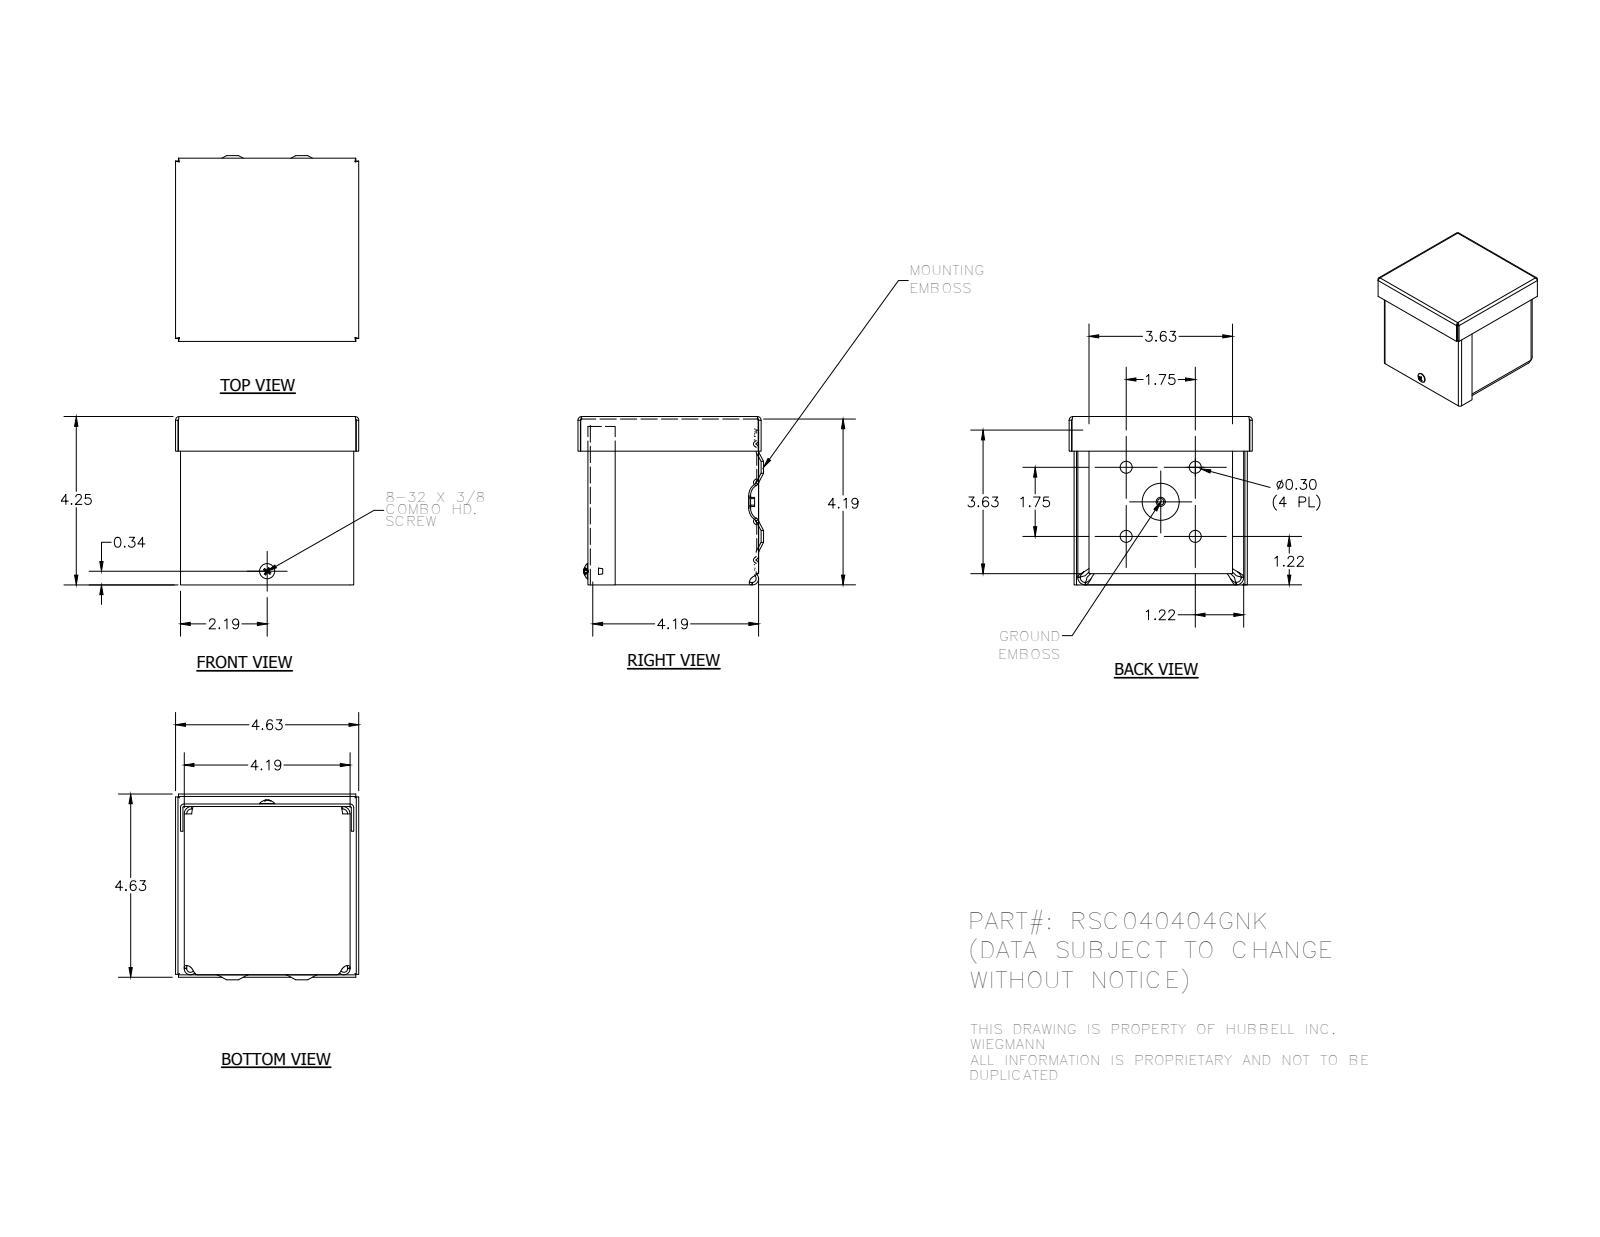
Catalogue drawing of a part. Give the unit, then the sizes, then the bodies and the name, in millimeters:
Units: millimetres
Overall size (bounding box): 119.09 × 117.47 × 107.96
Round holes (diameter × count): ⌀7.62 ×4, ⌀7.95 ×2, ⌀3.76 ×1, ⌀4.19 ×1
Round bosses / shafts (diameter × count): ⌀9.75 ×1, ⌀5.8 ×1, ⌀4.17 ×1
Partial cylindrical surfaces — rounded edges, fillets, slot ends (radius × count): R3.17 ×8, R4.75 ×8, R0.79 ×6, R2.37 ×6, R1.4 ×4, R1.57 ×4, R2.38 ×4, R2.97 ×4
Main face-to-face distances: 1.58, 104.79, 1.57, 106.37, 3.15, 107.94, 106.36, 107.93, 103.21, 106.35
Hole centre spacings: 31.34, 31.35, 44.32, 44.33, 62.69, 28.21, 28.25, 31.43
Volume: 161 195 mm³ · Surface area: 209 557 mm²
Bodies: 5 solids, 313 faces (128 planar, 64 cylindrical, 121 other)
Part name (STEP PRODUCT): RSC040404GNK_WRAP; RSC0404GNK_LID; RSC0404GNK_CAP; RSC0404GNK_BKP (+2 more)
STEP written by: Autodesk Inventor 2014 (AUTOMOTIVE_DESIGN)
